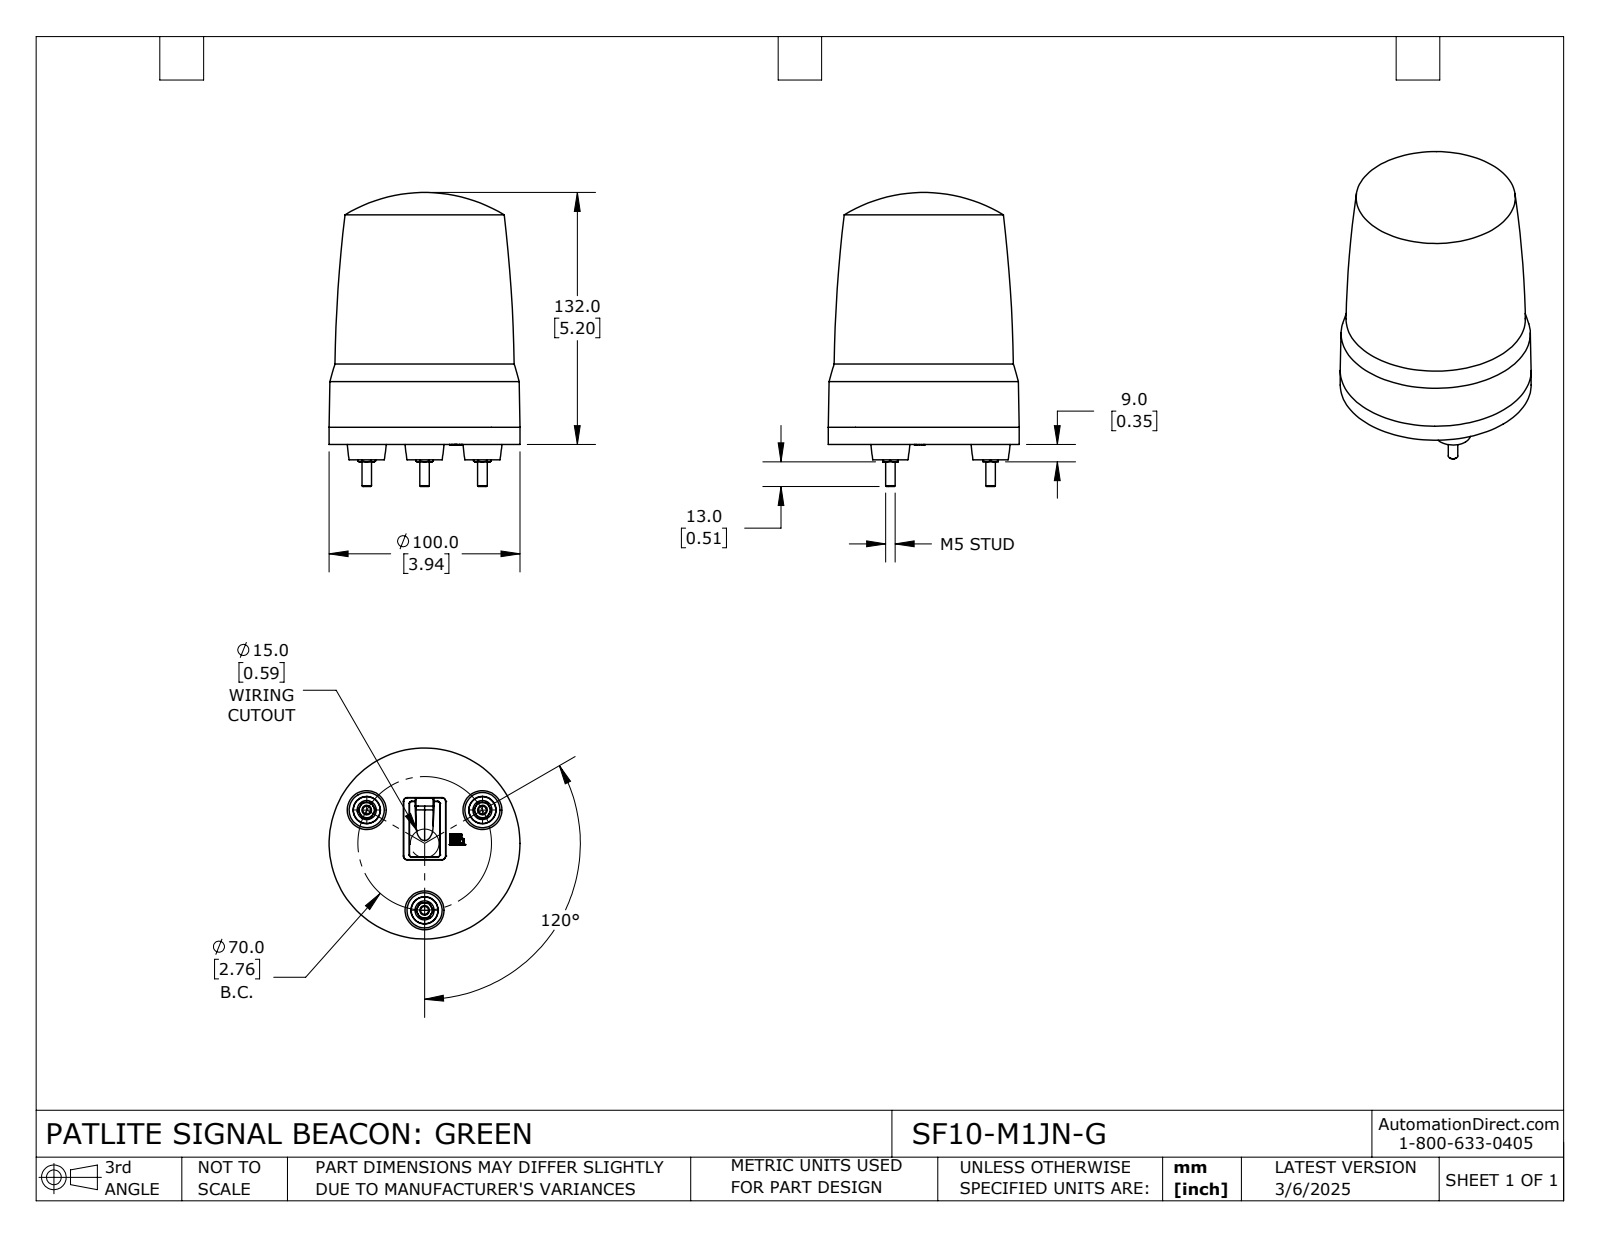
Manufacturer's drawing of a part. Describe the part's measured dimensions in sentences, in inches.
The part is named "SF10-M1JN-G". Its 3-D file was written by "SolidWorks 2024 (CONFIG_CONTROL_DESIGN)". It is 1 solid with 327 faces: 159 planar, 14 cylindrical and 154 other. Overall it measures 6.063 by 3.937 by 3.937 inches. Its volume is 52.48 cubic inches and its surface area 81.51 square inches. Round bosses or shafts: 3 of diameter 0.394, 3 of diameter 0.197, 1 of diameter 3.937. The main face-to-face distances are 0.315, 0.033, 0.348, 0.063, 0.411, 0.096, 0.15, 0.165, 0.199, 0.262.
